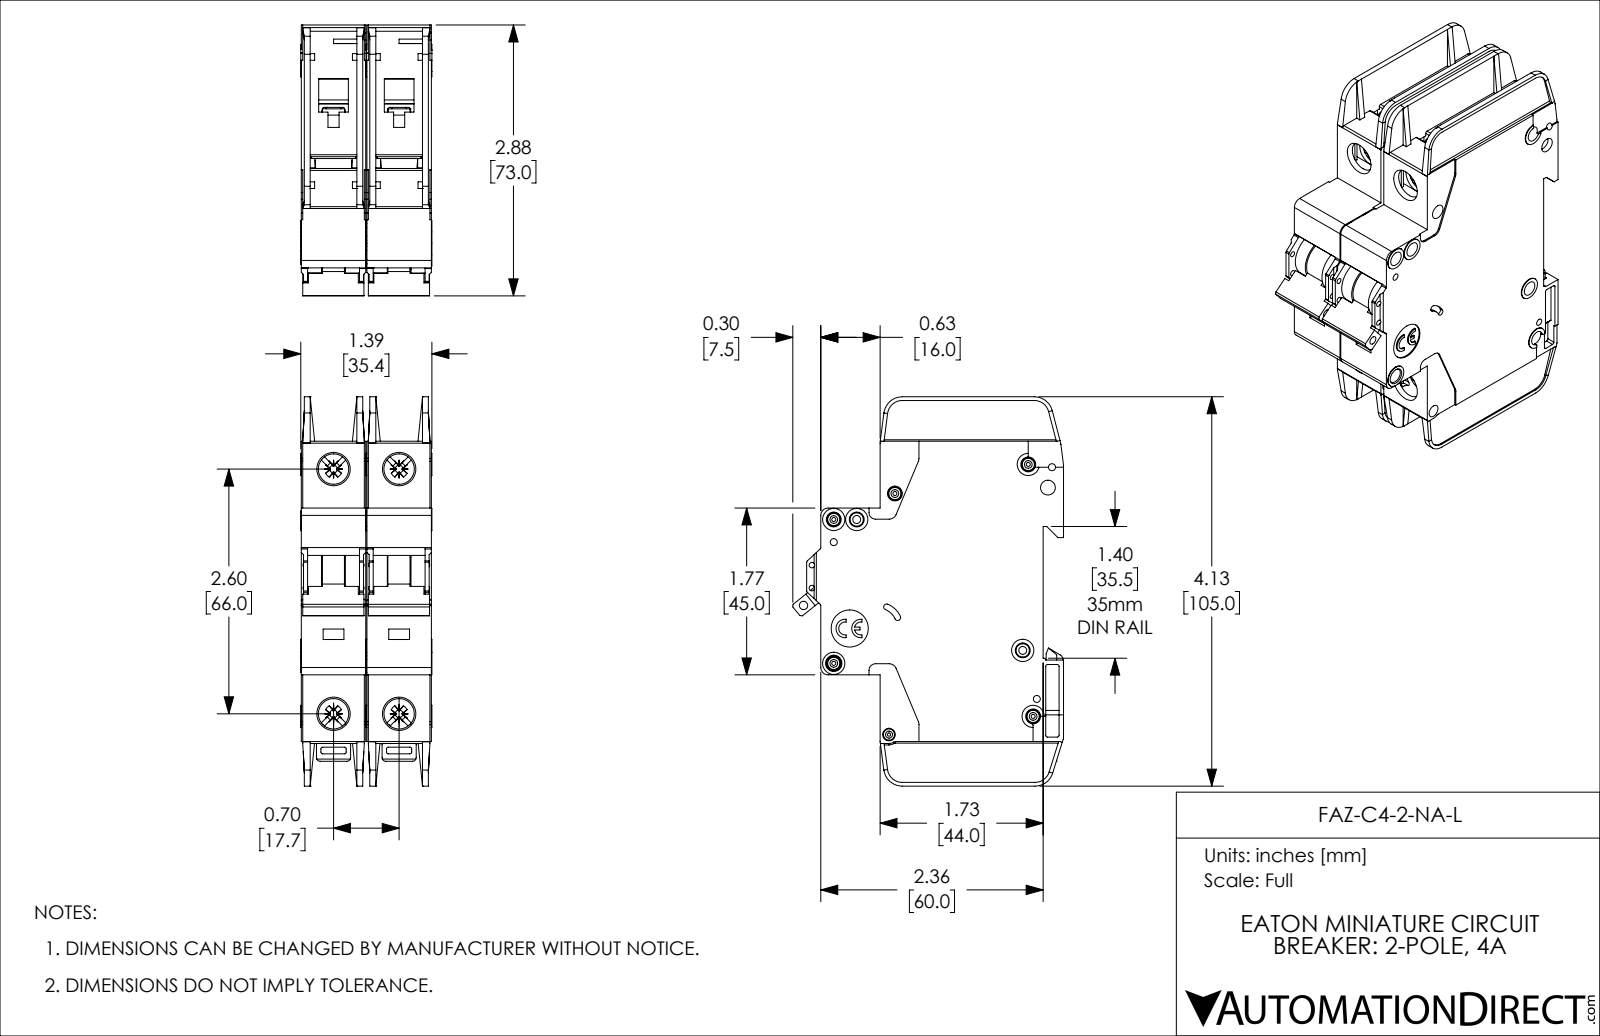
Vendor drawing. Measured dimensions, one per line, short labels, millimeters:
name: FAZ-C4-2-NA-L
written by: SolidWorks 2019 (AUTOMOTIVE_DESIGN)
unit: mm
bodies: 2 solids, 2254 faces (1342 planar, 714 cylindrical, 198 other)
size: 105 × 73.1 × 35.4
volume: 153 500 mm³; area: 52 910 mm²
holes: 8× ⌀4, 5× ⌀1.1, 4× ⌀1.9, 4× ⌀8.2, 2× ⌀1.5, 2× ⌀2.2, 1× ⌀0.9, 1× ⌀2.3, 1× ⌀2.5, 1× ⌀3.4, 1× ⌀10
bosses: 5× ⌀3.3, 4× ⌀6, 3× ⌀3, 2× ⌀2.5
rounds: 57× R0.5, 20× R0.4, 14× R1, 10× R2, 8× R1.1, 5× R0.2, 5× R5, 4× R0.3
face distances: 17.7, 1.2, 17.4, 15, 2.4, 16.2, 13.8, 35.1, 18.9, 16.5
hole spacings: 6.2, 13.6, 17.7, 22.1, 66, 68.3, 4.8, 5.1
